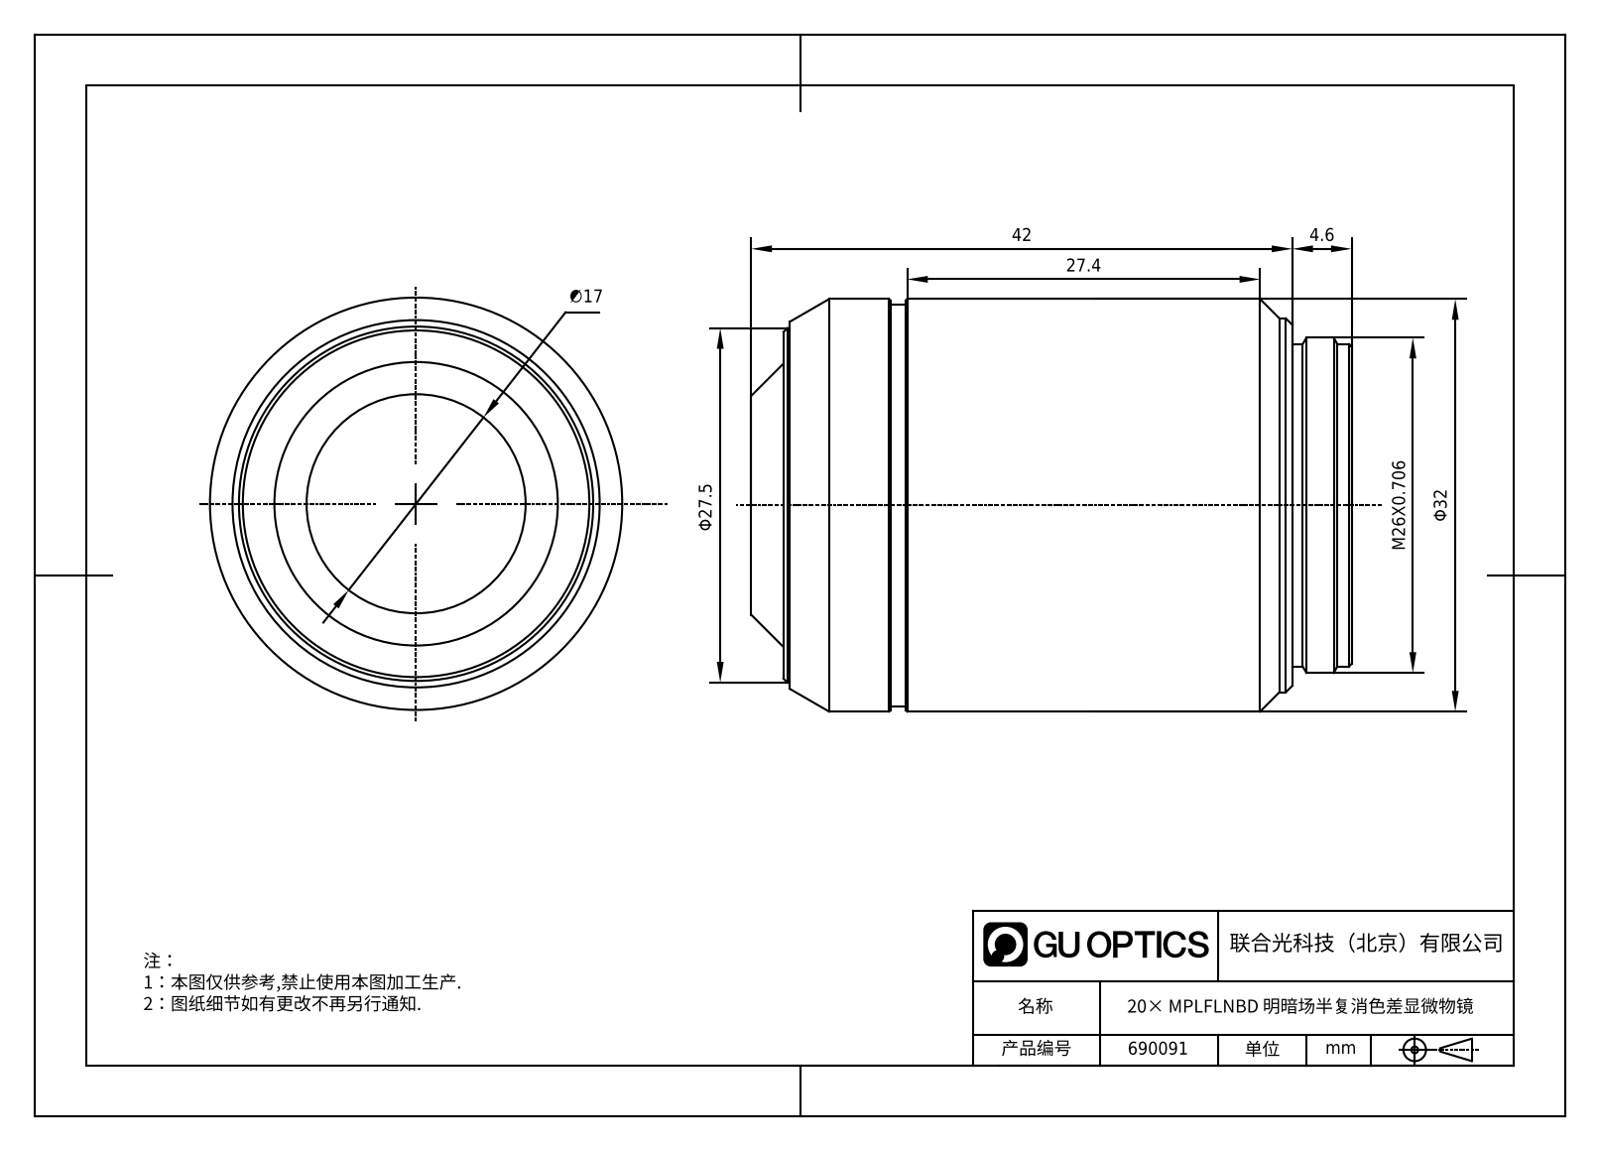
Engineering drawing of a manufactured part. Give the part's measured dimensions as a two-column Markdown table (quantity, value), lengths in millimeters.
| quantity | value |
| --- | --- |
| part name | 690091; 690091.stp; MPLFLN20XBD.stp |
| STEP written by | SolidWorks 2020 (CONFIG_CONTROL_DESIGN) |
| units | millimeters |
| bodies | 1 solid, 43 faces (7 planar, 16 cylindrical, 20 other) |
| overall size | 46.6 × 32 × 32 |
| volume | 34 192 mm³ |
| surface area | 5 825 mm² |
| round bosses / shafts (diameter × count) | 32 × 1, 31.2 × 1, 29 × 1, 27.5 × 1, 26 × 1, 25 × 1 |
| main face-to-face distances | 46.6, 2.5, 44.1, 42, 39.5, 4.6, 3, 0.5, 39, 43.6 |
